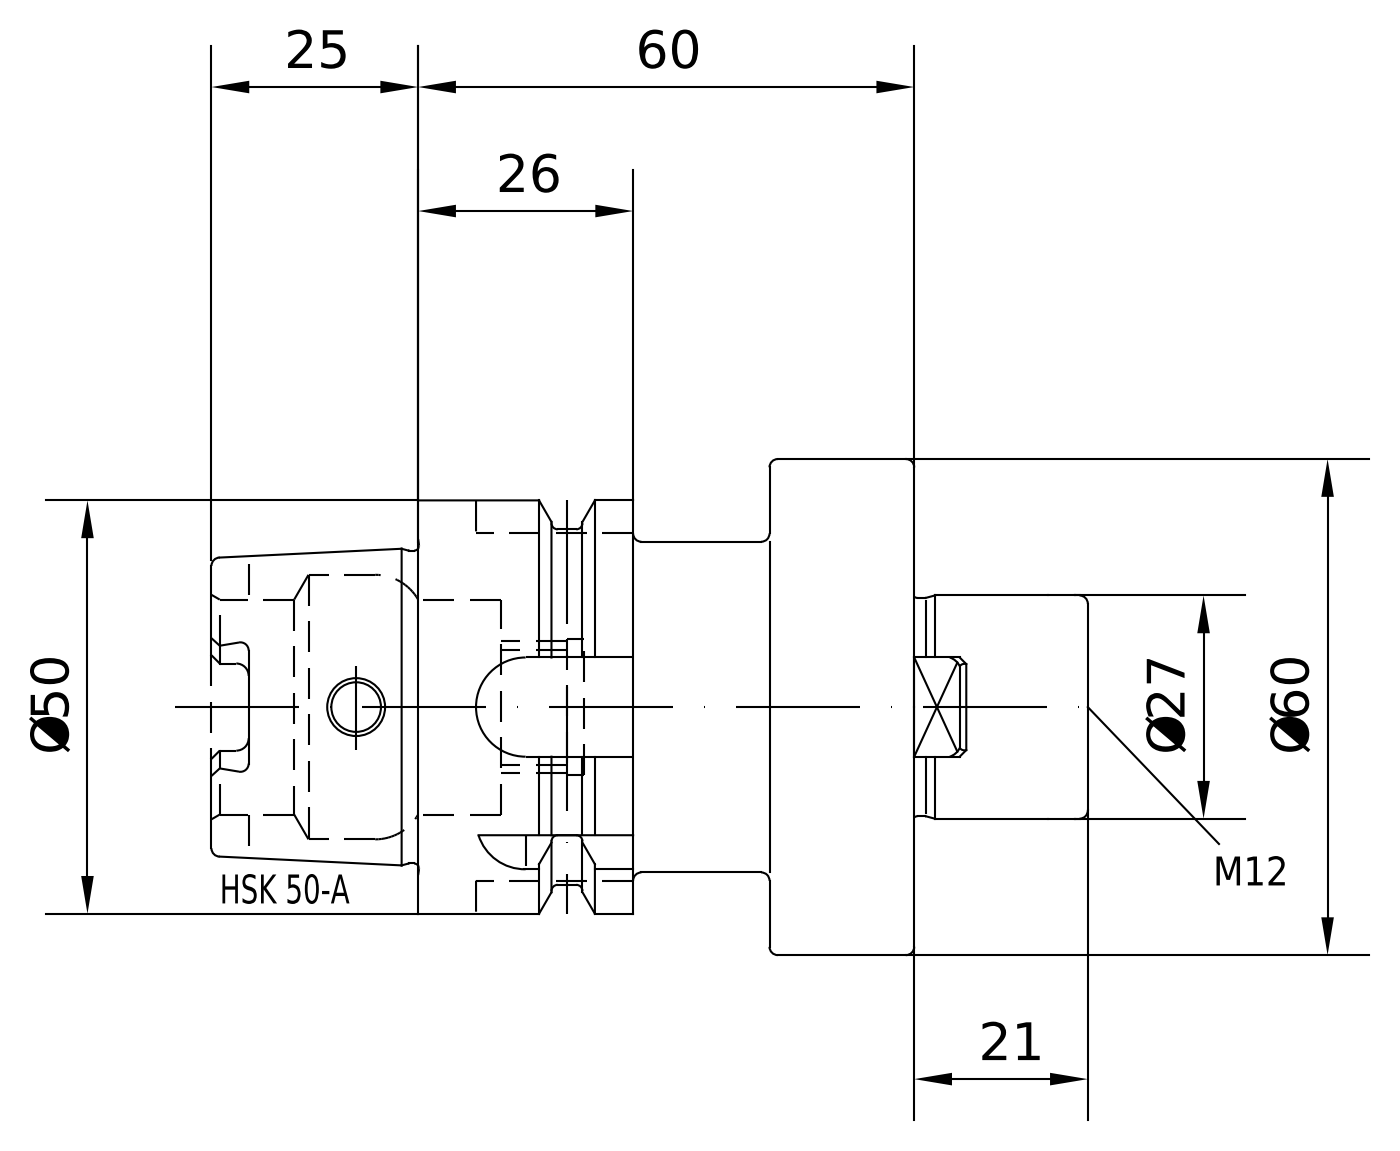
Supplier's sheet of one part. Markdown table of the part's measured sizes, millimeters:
| quantity | value |
| --- | --- |
| part name | A50-050-27 |
| STEP written by | PRO/ENGINEER BY PARAMETRIC TECHNOLOGY CORPORATION, 2010430 (CONFIG_CONTROL_DESIGN) |
| units | millimeters |
| bodies | 1 solid, 204 faces (75 planar, 51 cylindrical, 78 other) |
| overall size | 105.9 × 60 × 60 |
| volume | 130 357 mm³ |
| surface area | 26 820 mm² |
| round holes (diameter × count) | 6 × 1, 10 × 1, 10.2 × 1, 14 × 1, 16.32 × 1, 16.5 × 1, 26.04 × 1, 32.08 × 1 |
| round bosses / shafts (diameter × count) | 60 × 1, 50 × 1, 42.95 × 1, 40 × 1, 37.91 × 1, 27 × 1 |
| partial cylindrical surfaces (radius × count) | 1.4 × 6, 2.38 × 4, 6 × 3, 6.02 × 1 |
| main face-to-face distances | 17.55, 42.45, 60, 25.95, 16.5, 34.05, 81, 55.05, 38.55, 21 |
